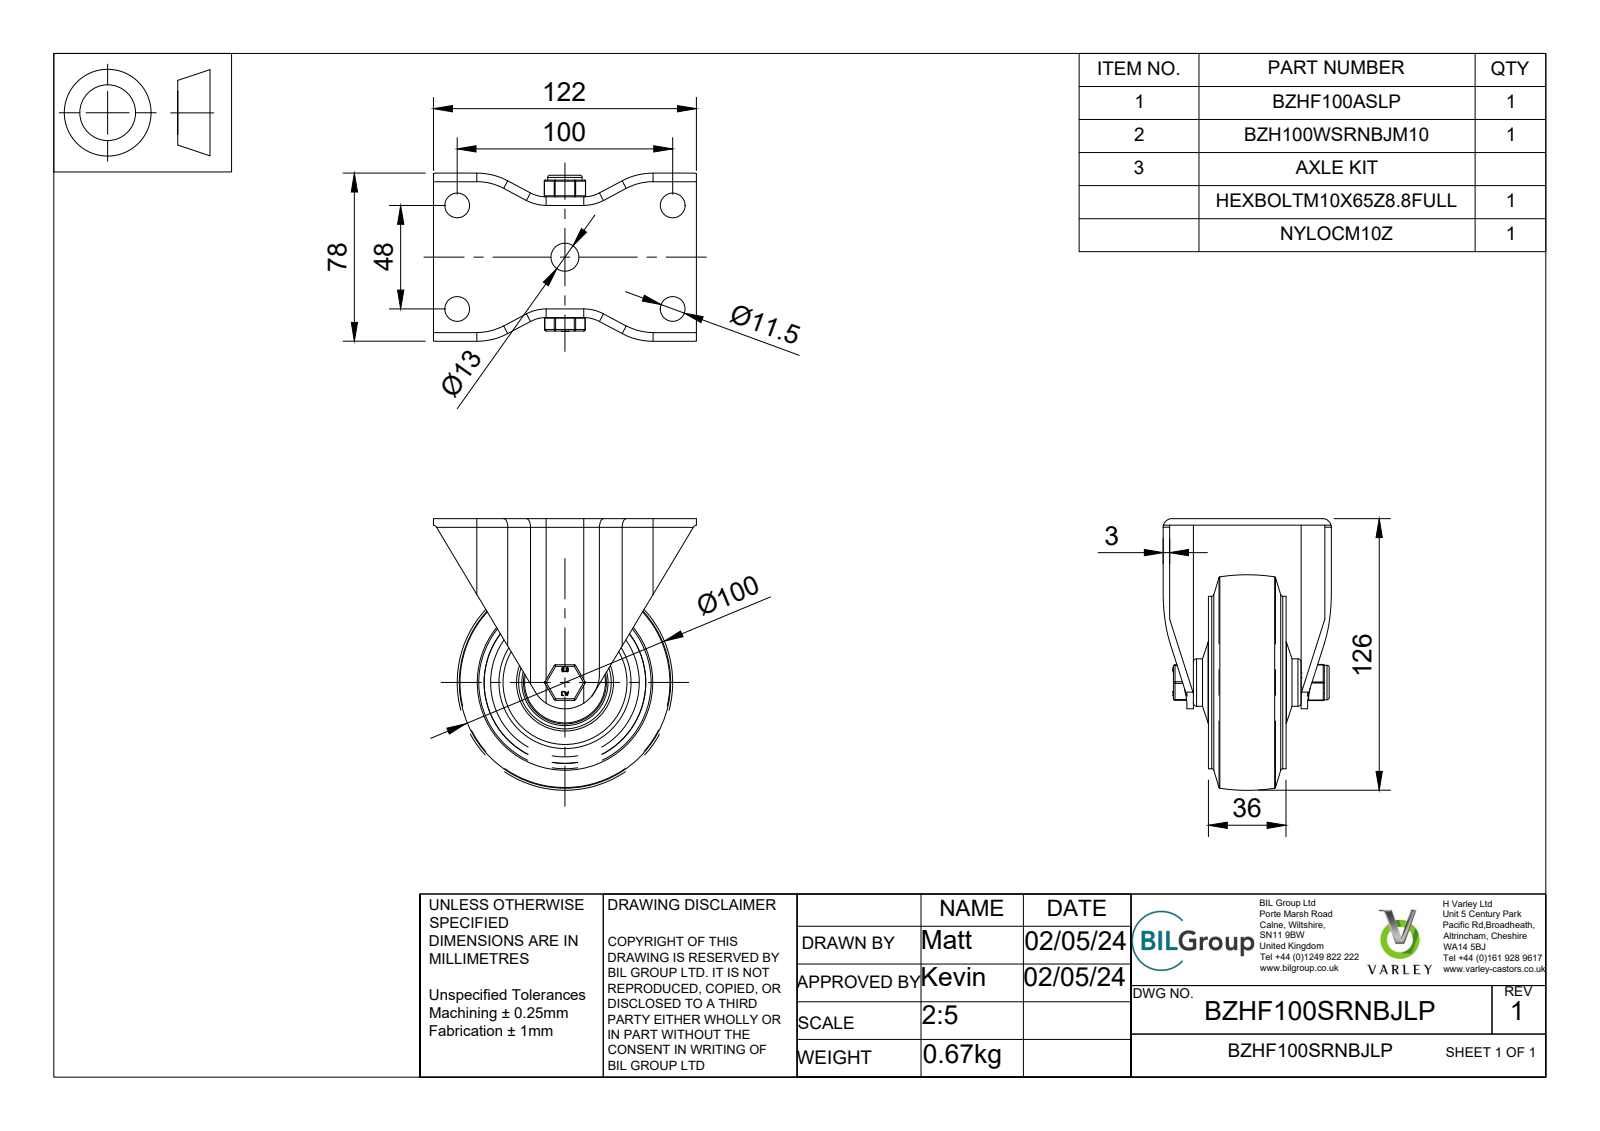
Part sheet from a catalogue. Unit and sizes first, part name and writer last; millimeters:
Units: millimetres
Overall size (bounding box): 126 × 122 × 78
Round holes (diameter × count): ⌀11.5 ×4, ⌀10 ×1, ⌀10.2 ×1, ⌀10.8 ×1, ⌀12 ×1, ⌀13 ×1, ⌀15 ×1, ⌀20 ×1, ⌀22.5 ×1, ⌀26 ×1, ⌀30 ×1, ⌀31 ×1
Round bosses / shafts (diameter × count): ⌀80 ×1, ⌀43 ×1, ⌀38.5 ×1, ⌀35 ×1, ⌀30.5 ×1, ⌀28 ×1, ⌀23 ×1, ⌀22 ×1
Partial cylindrical surfaces — rounded edges, fillets, slot ends (radius × count): R0.5 ×18, R0.75 ×12, R4 ×8, R15.5 ×4, R30.5 ×4, R2 ×2, R12 ×1, R13.75 ×1
Main face-to-face distances: 3, 11, 64, 21, 34.66, 8, 53, 10, 31.66, 33
Hole centre spacings: 55.46, 48, 100, 110.92
Volume: 248 049 mm³ · Surface area: 122 457 mm²
Bodies: 21 solids, 743 faces (259 planar, 222 cylindrical, 262 other)
Part name (STEP PRODUCT): BZHF100SRNBJLP v3; BZHF100ASLP - 50 v1; ZINC PLATED PRESSED STEEL BRACKET; BZH100WSRNBJM10 v1 (+7 more)
STEP written by: Autodesk Translation Framework v12.20.1.177 (AUTOMOTIVE_DESIGN)
